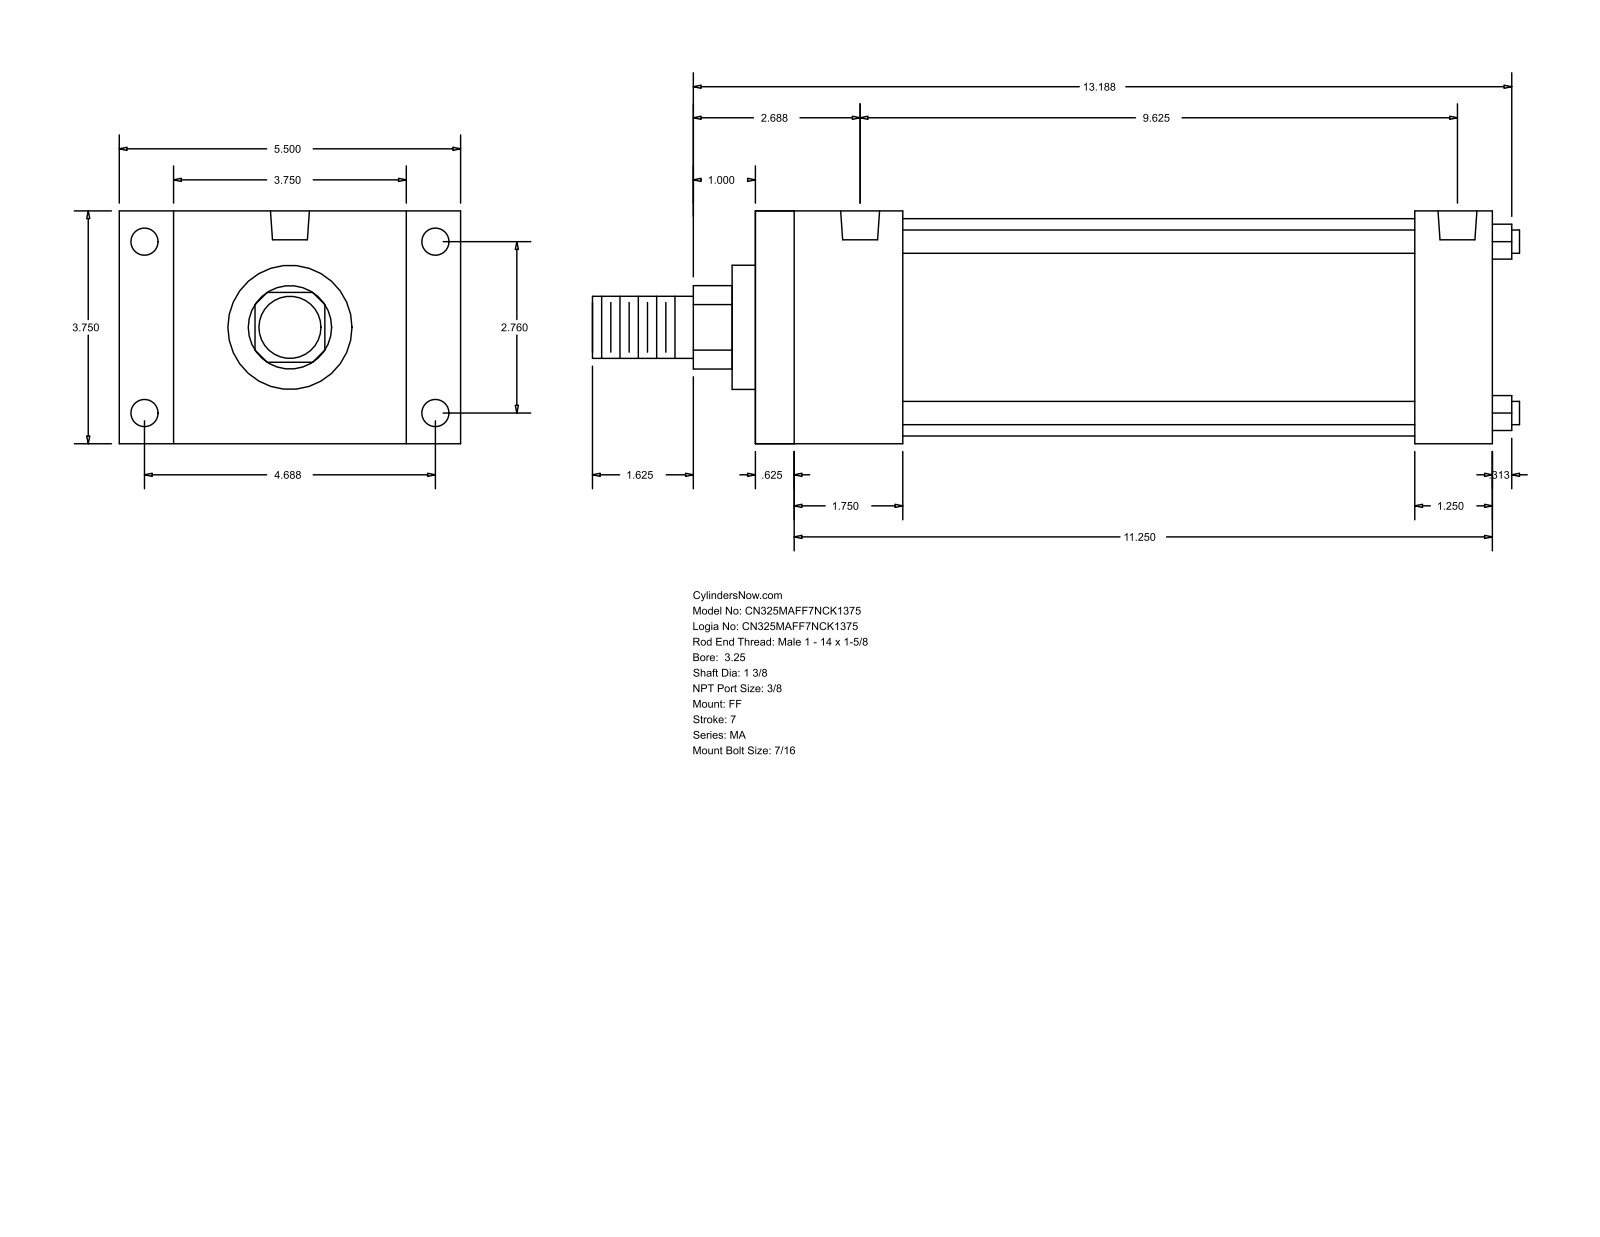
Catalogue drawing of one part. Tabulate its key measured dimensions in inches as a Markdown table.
| quantity | value |
| --- | --- |
| part name | MA_FF__0325_1.375 |
| STEP written by | GSSL Pune (CONFIG_CONTROL_DESIGN) |
| units | inches |
| bodies | 0 solids, 92 faces (64 planar, 28 cylindrical, 0 other) |
| overall size | 14.937 × 5.5 × 3.75 |
| round holes (diameter × count) | 0.437 × 8, 0.627 × 2 |
| round bosses / shafts (diameter × count) | 0.375 × 4, 3.5 × 1, 2 × 1, 1.375 × 1, 1 × 1 |
| partial cylindrical surfaces (radius × count) | 0.672 × 1 |
| main face-to-face distances | 3.75, 11.875, 0.625, 11.25, 0.875, 4.625, 2.375, 10.625, 1.75, 10 |
| hole center spacings | 2.76, 4.687, 5.439, 9.25, 0.187, 0.188, 9.437, 9.438 |
